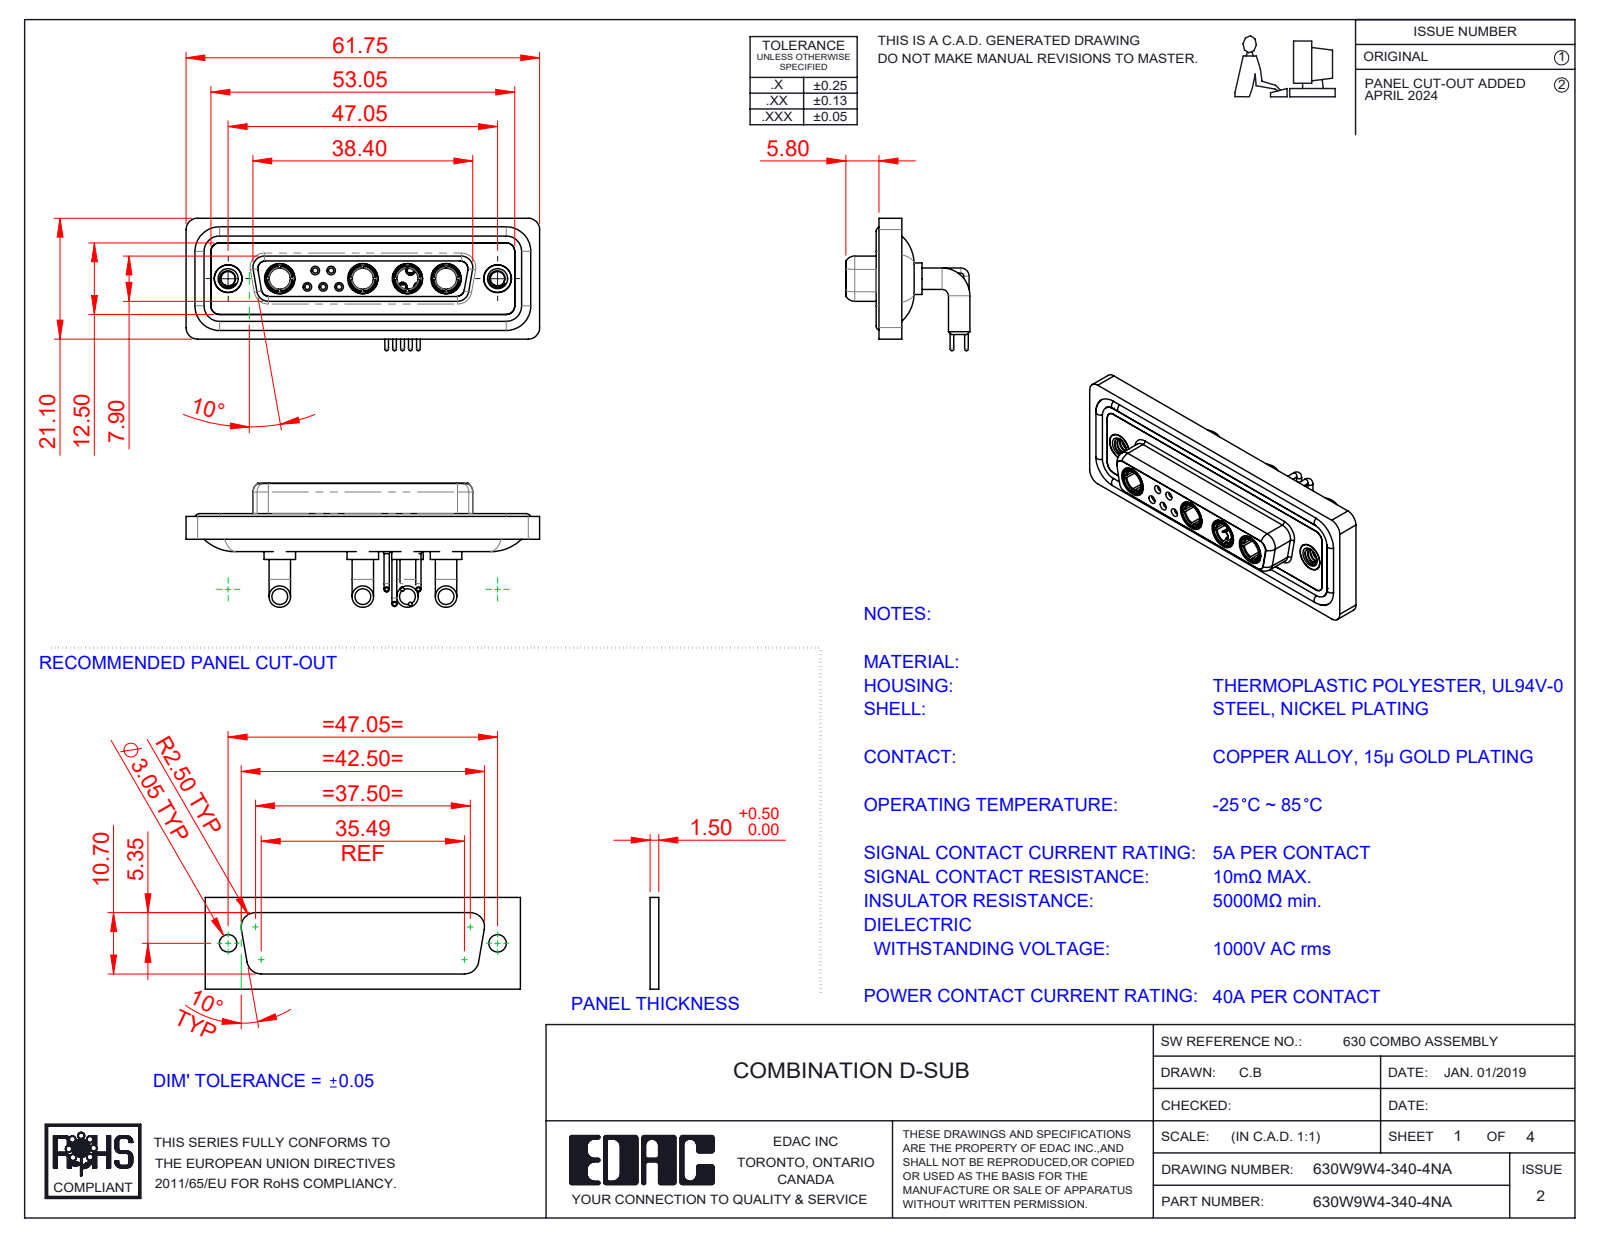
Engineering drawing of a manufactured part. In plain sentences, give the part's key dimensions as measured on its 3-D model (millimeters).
The part is named "630Combo Waterproof Housing_25 Contacts; 630Combo Contact Row 1_50 Contacts; 630Combo Shell Rear_25 Contacts; 630Combo Contact Row 2_50 Contacts (+5 more)". Its 3-D file was written by "SolidWorks 2023 (CONFIG_CONTROL_DESIGN)". It is 20 solids with 957 faces: 296 planar, 401 cylindrical and 260 other. Overall it measures 61.75 by 23.12 by 21.68 millimeters. Its volume is 8 735 cubic millimeters and its surface area 14 225 square millimeters. Round holes: 6 of diameter 4.85, 5 of diameter 0.9, 5 of diameter 1.1, 5 of diameter 1.5, 5 of diameter 2, 4 of diameter 3.7, 4 of diameter 5.3, 3 of diameter 1.6, 2 of diameter 1.7, 2 of diameter 2.5, 2 of diameter 4, 2 of diameter 4.05. Round bosses or shafts: 10 of diameter 0.9, 9 of diameter 1.6, 8 of diameter 3.75, 5 of diameter 2, 5 of diameter 1.5, 5 of diameter 0.65, 4 of diameter 5.5, 4 of diameter 5.2. Partial cylindrical surfaces (rounded edges, fillets, slot ends): 18 of radius 1.5, 18 of radius 2, 8 of radius 1.35, 8 of radius 1.6, 4 of radius 0.25, 4 of radius 0.5, 4 of radius 0.6, 4 of radius 0.65. The main face-to-face distances are 0.4, 1.8, 4.1, 1.1, 1.6, 2.5, 3.1, 3.7, 1.5, 1.4. The hole center spacings are 3.16, 2.77, 5.04, 13.85, 11.08, 12.79, 15.5, 5.54.
